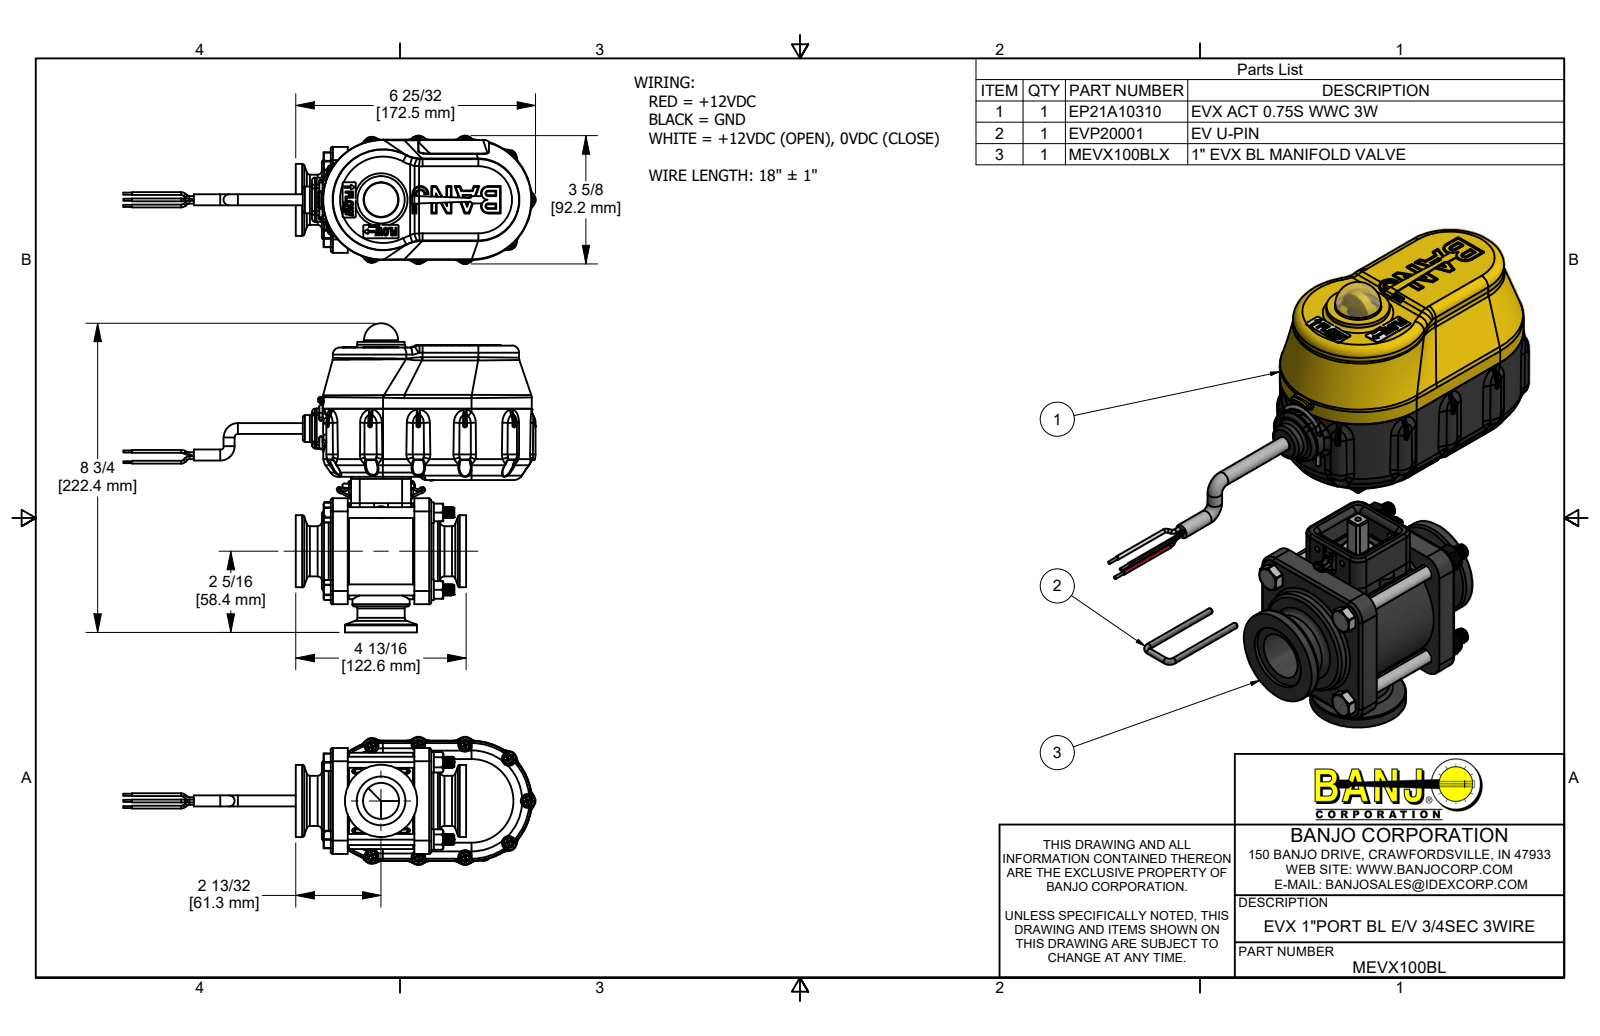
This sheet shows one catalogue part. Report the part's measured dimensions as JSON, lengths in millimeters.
{"part_name": "MEVX100BL; MEVX100BLX; MEVX10354AB; MEVX10354ABX (+8 more)", "step_written_by": "Autodesk Inventor 2019 (AUTOMOTIVE_DESIGN)", "units": "millimeters", "bodies": {"solids": 98, "faces": 11857, "planar": 3137, "cylindrical": 3477, "other": 5243}, "overall_size": [296.8, 222.4, 92.2], "volume_mm3": 877400, "surface_area_mm2": 387900, "round_holes": [[2.4, 11], [3.8, 11], [2, 7], [2.7, 4], [3.2, 4], [3.4, 4], [3.5, 4], [3.8, 4], [3.8, 4], [4.3, 4], [6.4, 4], [8.2, 4]], "round_bosses_or_shafts": [[6.8, 60], [6.4, 17], [2, 15], [3.6, 11], [2.7, 11], [2.2, 11], [1.5, 6], [8, 5]], "partial_cylinders_radius": [[0.3, 180], [1, 145], [0.3, 84], [0.5, 72], [0.1, 53], [1.5, 42], [0.8, 38], [2, 28]], "face_to_face_distances": [2.5, 65.2, 12.2, 1.4, 5.4, 1.5, 3.8, 60.1, 3.2, 48.2], "hole_center_spacings": [39.3, 42.2, 48, 55.6, 67.5, 68.3, 69, 83.7]}
